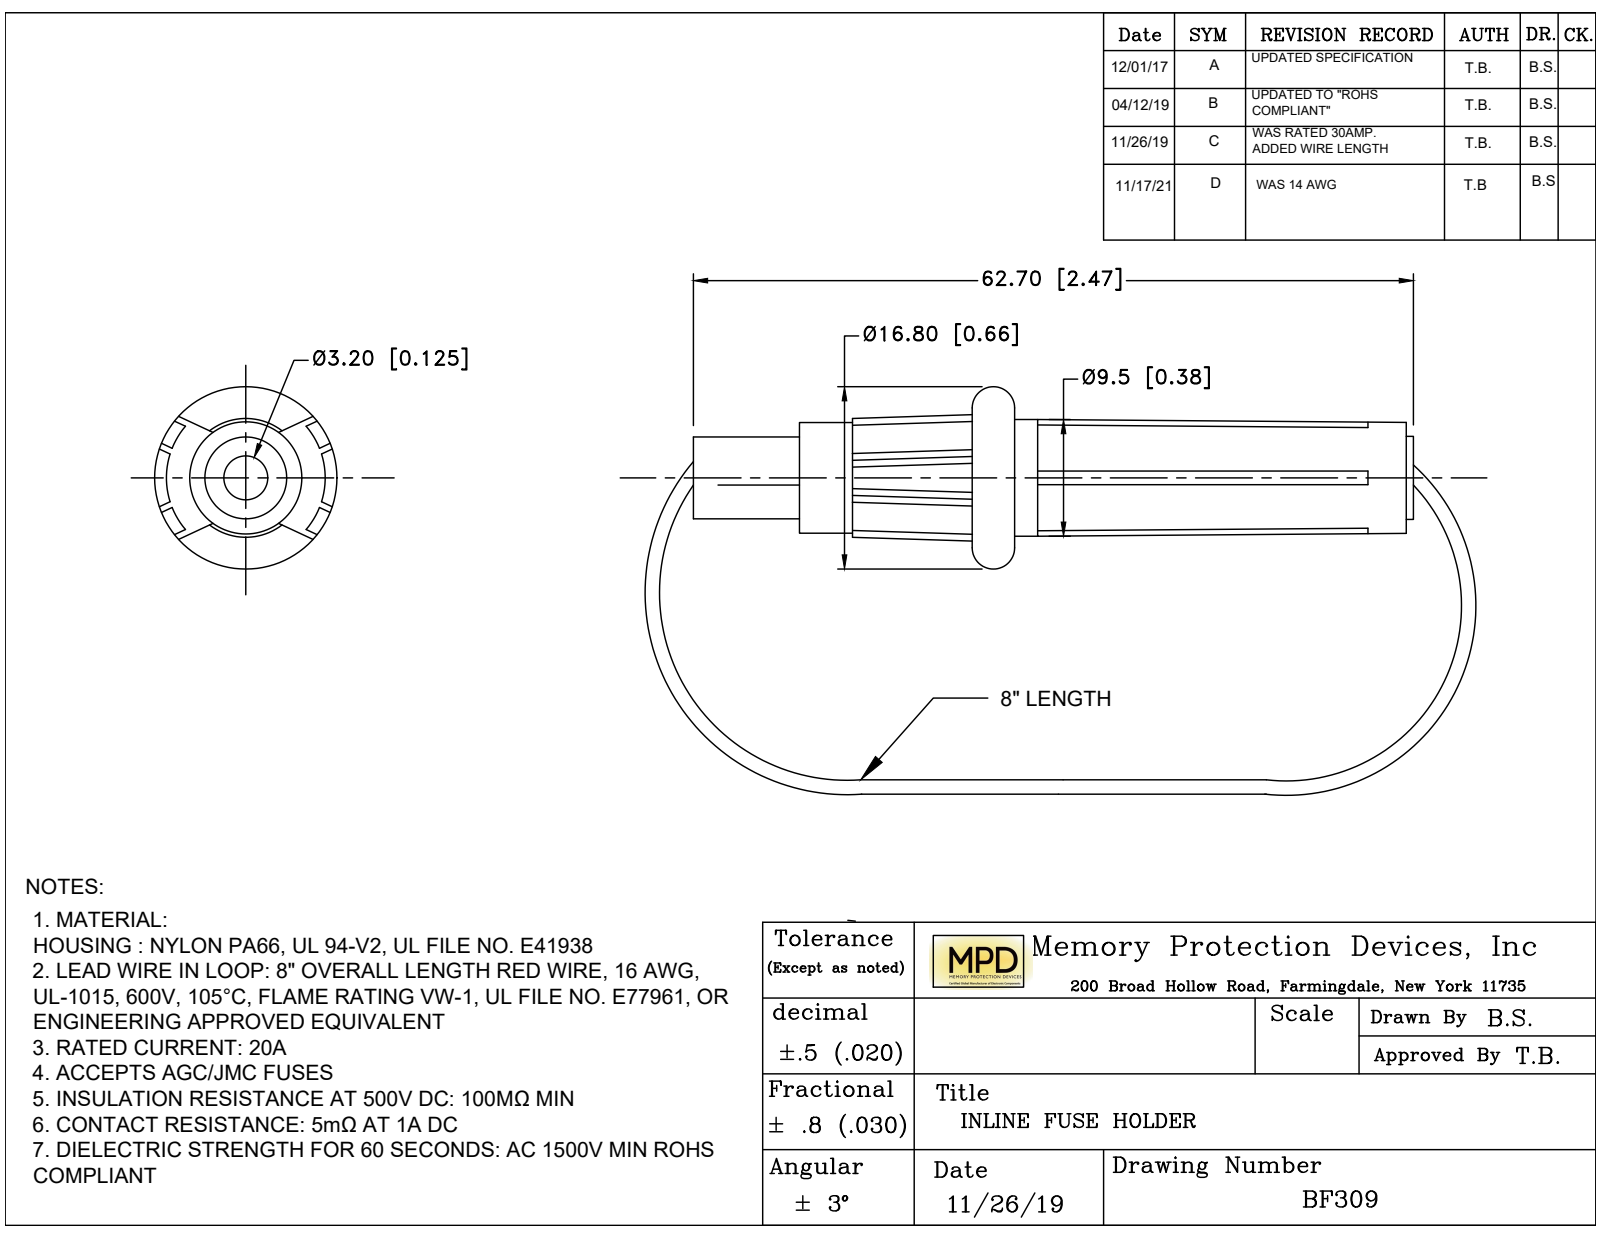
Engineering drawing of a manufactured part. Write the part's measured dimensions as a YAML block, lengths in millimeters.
part_name: "BF309"
step_written_by: "SolidWorks 2017 (AUTOMOTIVE_DESIGN)"
units: millimeters
bodies: {solids: 3, faces: 83, planar: 44, cylindrical: 14, other: 25}
overall_size: [95.9, 40, 16.8]
volume: 6073
surface_area: 4272
round_bosses_or_shafts:
  - {diameter: 9.8, count: 1}
  - {diameter: 9.5, count: 1}
  - {diameter: 7, count: 1}
  - {diameter: 3.2, count: 1}
face_to_face_distances: [3.43, 4.57, 1.14, 8, 2, 34.7, 62.7, 28, 0.5, 2.66]
